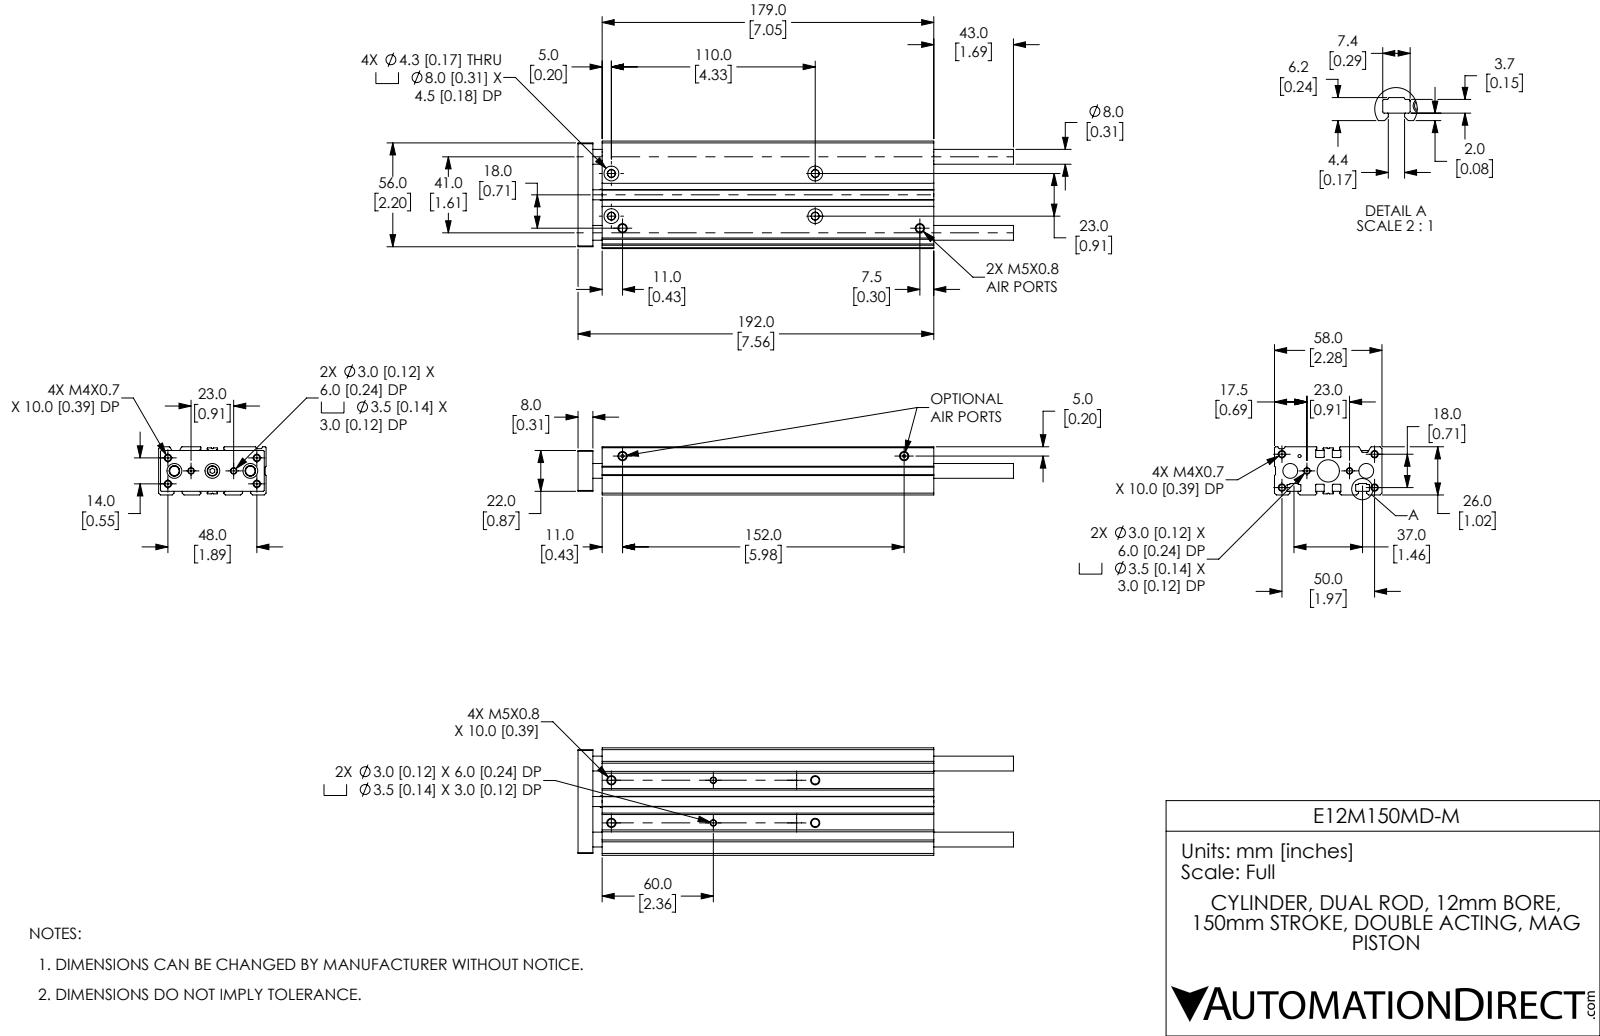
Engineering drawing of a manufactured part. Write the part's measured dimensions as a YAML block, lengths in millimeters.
part_name: "E12M150MD-M; E12M150MD-M_ENDPLATE; E12M150MD-D_BODY"
step_written_by: "SolidWorks 2019 (CONFIG_CONTROL_DESIGN)"
units: millimeters
bodies: {solids: 5, faces: 413, planar: 137, cylindrical: 188, other: 88}
overall_size: [235, 58, 26]
volume: 230989
surface_area: 86296
round_holes:
  - {diameter: 3.24, count: 8}
  - {diameter: 4.13, count: 8}
  - {diameter: 8, count: 7}
  - {diameter: 3, count: 4}
  - {diameter: 3.5, count: 4}
  - {diameter: 4.3, count: 4}
  - {diameter: 1.67, count: 3}
  - {diameter: 4, count: 3}
  - {diameter: 5.59, count: 2}
  - {diameter: 8, count: 1}
  - {diameter: 12, count: 1}
  - {diameter: 12, count: 1}
round_bosses_or_shafts:
  - {diameter: 6, count: 1}
  - {diameter: 5.59, count: 1}
partial_cylinders:
  - {radius: 0.4, count: 20}
  - {radius: 0.2, count: 18}
  - {radius: 0.25, count: 8}
  - {radius: 0.3, count: 6}
  - {radius: 0.5, count: 4}
face_to_face_distances: [26, 58, 5.8, 9, 20.2, 26.8, 31.2, 22.2, 35.8, 4.6]
hole_center_spacings: [2.24, 7.83, 10.06, 14.33, 16.03, 16.22, 23, 25]
